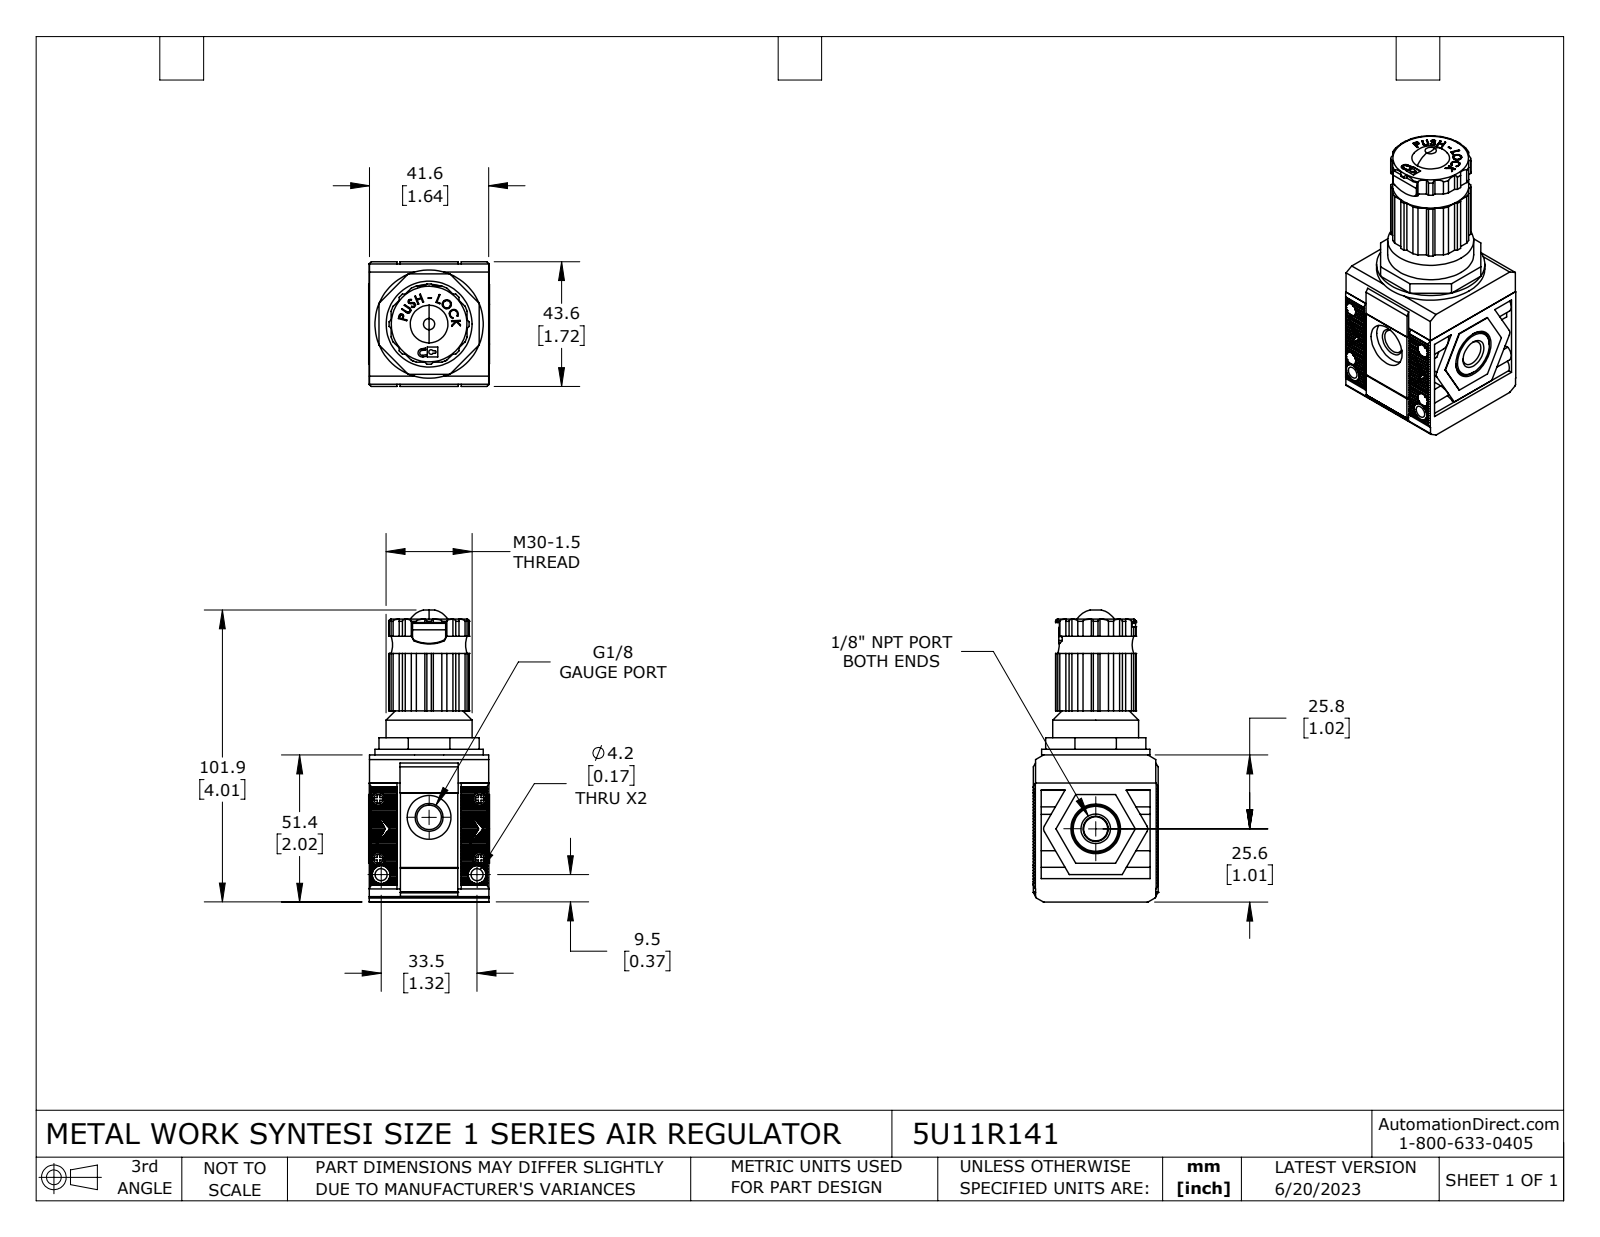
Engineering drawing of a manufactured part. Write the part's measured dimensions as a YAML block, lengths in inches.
part_name: "5U11R141"
step_written_by: "SolidWorks 2021 (CONFIG_CONTROL_DESIGN)"
units: inches
bodies: {solids: 13, faces: 1382, planar: 967, cylindrical: 300, other: 115}
overall_size: [4.016, 1.717, 1.661]
volume: 7.664
surface_area: 60.55
round_holes:
  - {diameter: 0.083, count: 4}
  - {diameter: 0.118, count: 4}
  - {diameter: 0.185, count: 4}
  - {diameter: 0.138, count: 2}
  - {diameter: 0.165, count: 2}
  - {diameter: 0.094, count: 1}
  - {diameter: 0.252, count: 1}
  - {diameter: 0.337, count: 1}
  - {diameter: 0.602, count: 1}
  - {diameter: 1.117, count: 1}
round_bosses_or_shafts:
  - {diameter: 0.181, count: 4}
  - {diameter: 0.102, count: 4}
  - {diameter: 0.244, count: 2}
  - {diameter: 1.488, count: 1}
  - {diameter: 1.26, count: 1}
  - {diameter: 1.181, count: 1}
  - {diameter: 0.898, count: 1}
  - {diameter: 0.717, count: 1}
partial_cylinders:
  - {radius: 0.024, count: 4}
  - {radius: 0.122, count: 4}
  - {radius: 0.059, count: 3}
  - {radius: 0.008, count: 2}
  - {radius: 0.051, count: 2}
  - {radius: 0.079, count: 2}
  - {radius: 0.016, count: 1}
  - {radius: 0.018, count: 1}
face_to_face_distances: [0.386, 1.638, 0.307, 1.339, 2.024, 1.642, 0.059, 1.673, 1.654, 0.043]
hole_center_spacings: [0.222, 0.362, 0.742, 0.785, 0.823, 0.9, 1.027, 1.042]
